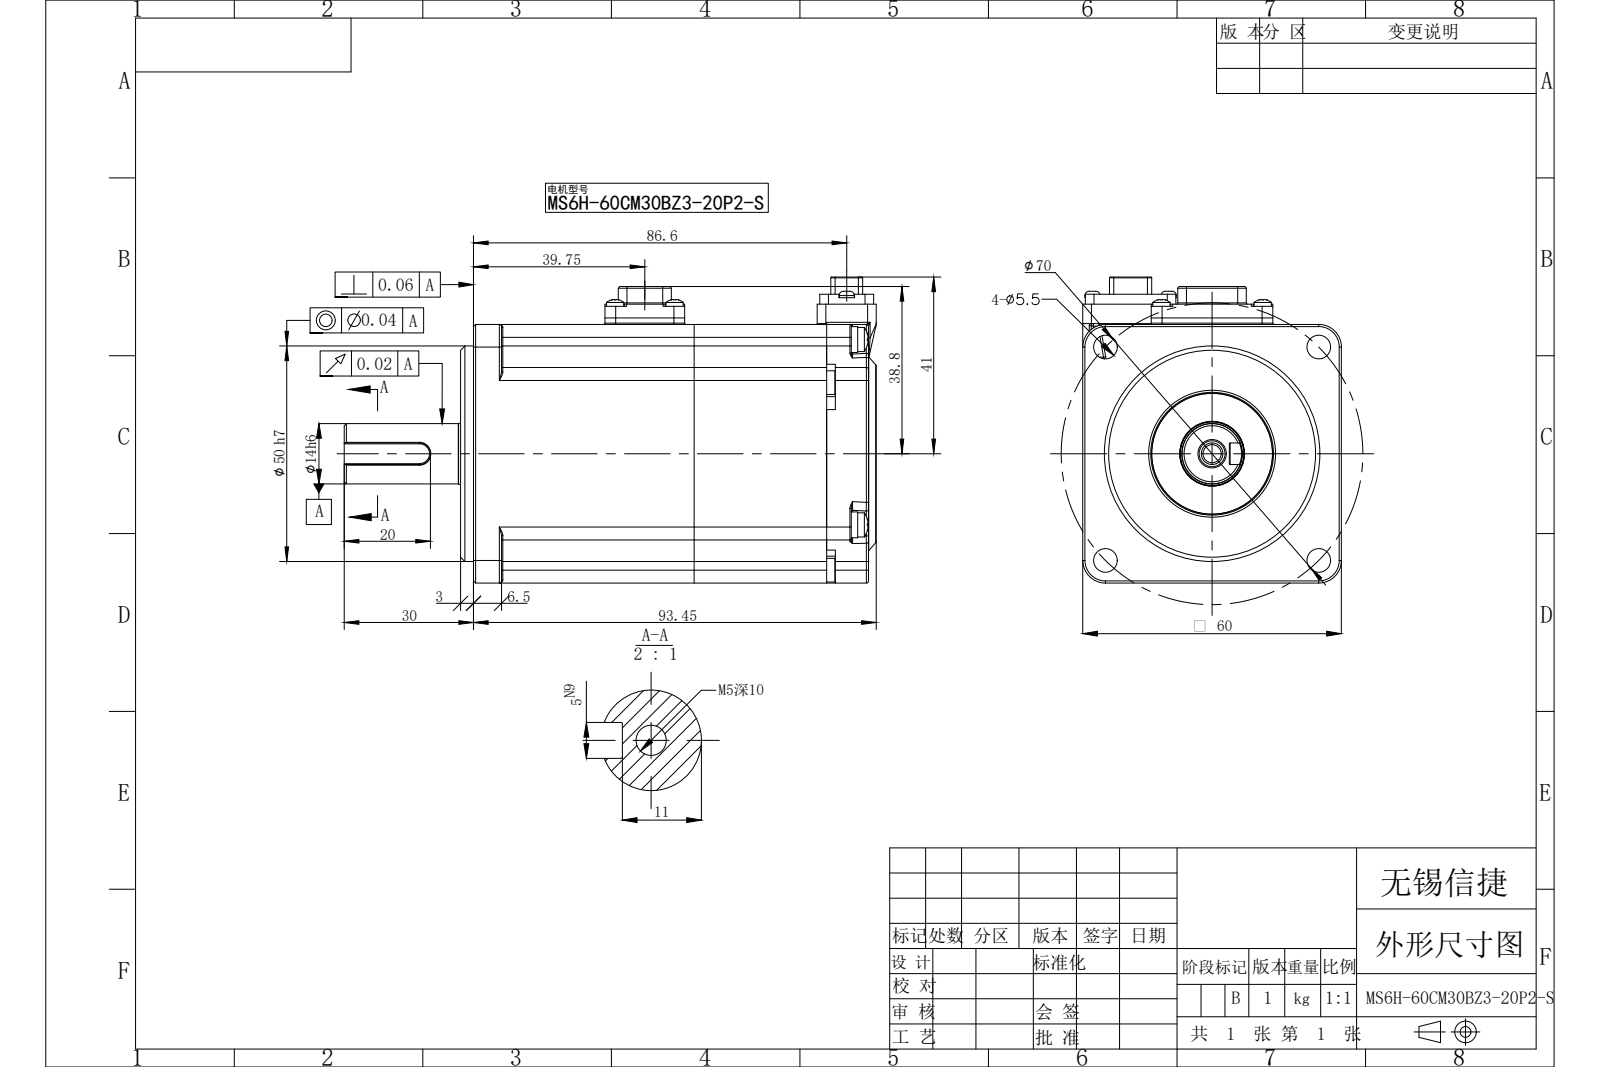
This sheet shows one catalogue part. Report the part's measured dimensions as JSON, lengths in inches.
{"part_name": "MS6H-60CM30BZ3-20P2-S", "step_written_by": "SolidWorks 2022 (CONFIG_CONTROL_DESIGN)", "units": "inches", "bodies": {"solids": 0, "faces": 792, "planar": 365, "cylindrical": 258, "other": 169}, "overall_size": [4.86, 2.795, 2.362], "round_holes": [[0.083, 4], [0.217, 4], [0.063, 2], [0.165, 1], [0.197, 1], [0.591, 1]], "round_bosses_or_shafts": [[0.236, 4], [0.22, 4], [0.217, 4], [0.157, 4], [0.138, 2], [1.969, 1], [1.102, 1], [0.551, 1]], "partial_cylinders_radius": [[0.02, 40], [0.012, 36], [0.008, 20], [0.118, 17], [0.079, 16], [0.039, 5], [0.098, 5], [0.024, 4]], "face_to_face_distances": [2.362, 0.453, 3.344, 0.118, 3.226, 3.679, 3.797, 0.071, 0.382, 0.394], "hole_center_spacings": [1.378, 1.949, 0.315, 0.654, 0.726, 2.756, 0.925, 1.688]}
